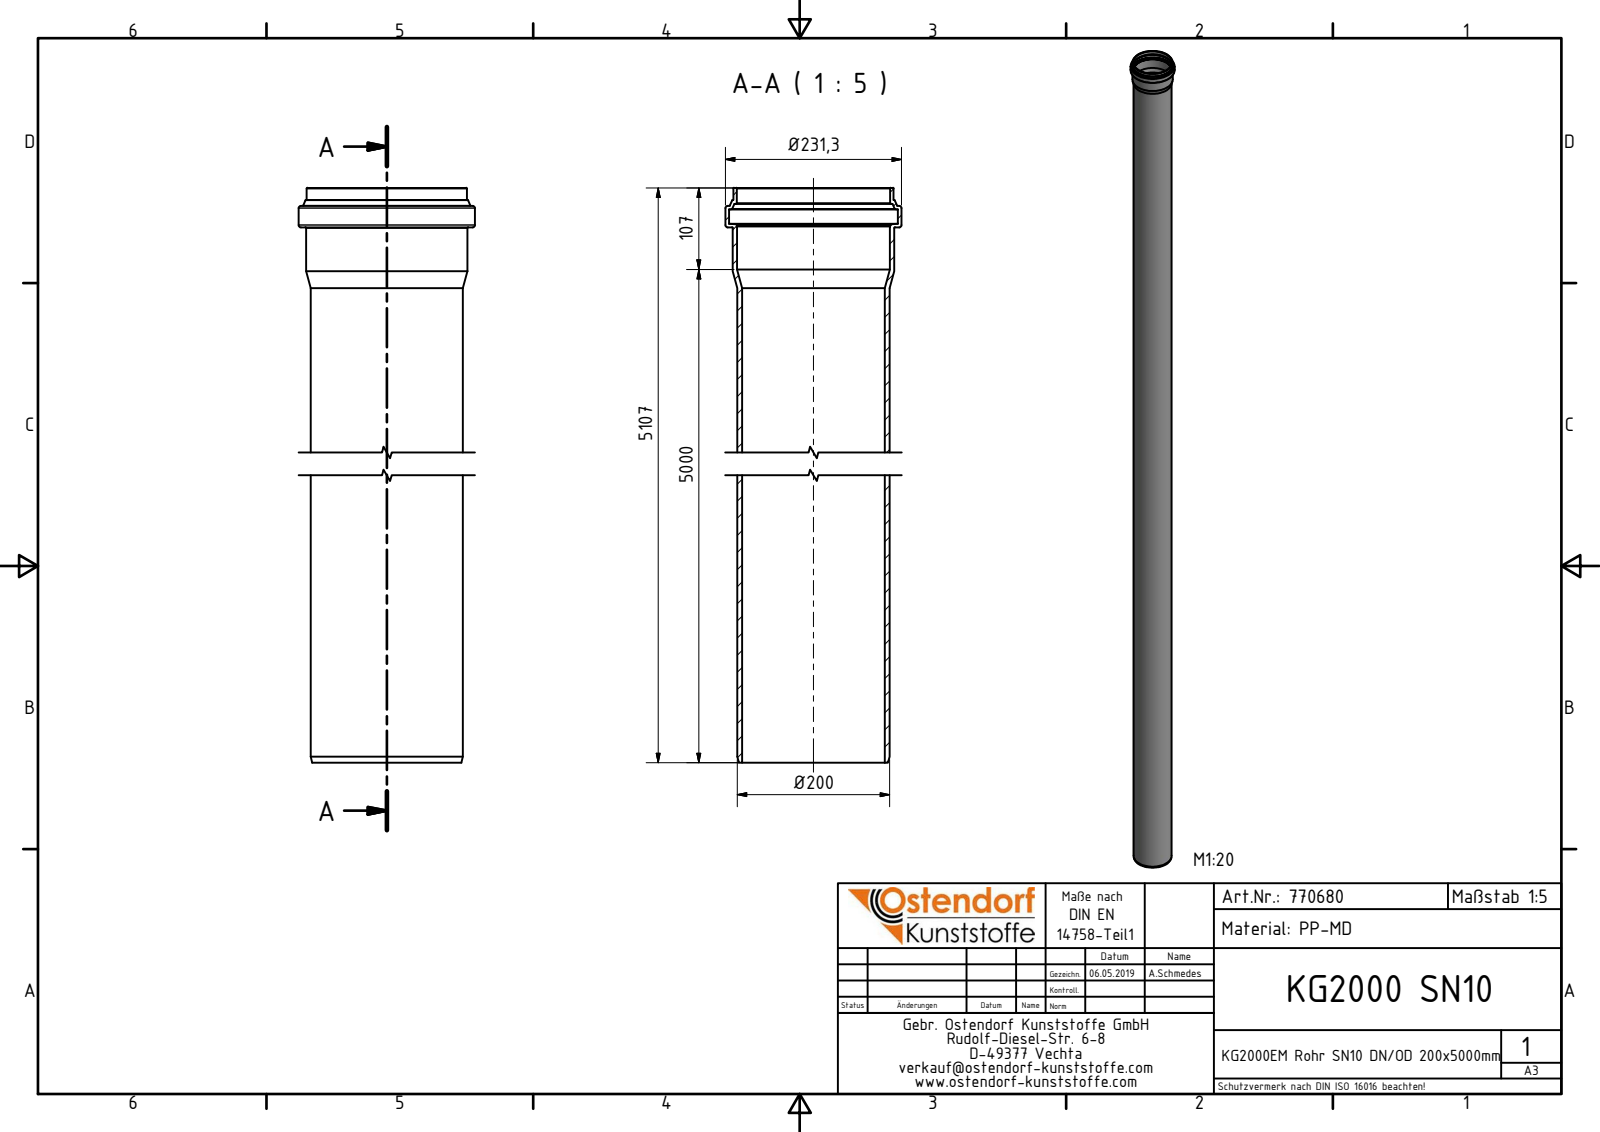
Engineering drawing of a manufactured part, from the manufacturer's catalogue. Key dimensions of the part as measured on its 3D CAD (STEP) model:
Part name (STEP PRODUCT): 770680 KG2000EM Rohr SN10 DN-OD200x5000
STEP written by: Autodesk Inventor 2016 (AUTOMOTIVE_DESIGN)
Units: millimetres
Bodies: 1 solid, 37 faces (6 planar, 9 cylindrical, 22 other)
Overall size (bounding box): 5107 × 231.3 × 231.3
Volume: 19 290 000 mm³ · Surface area: 6 258 000 mm²
Round holes (diameter × count): ⌀187.6 ×1, ⌀200.8 ×1, ⌀201 ×1, ⌀221.9 ×1
Round bosses / shafts (diameter × count): ⌀231.3 ×1, ⌀212 ×1, ⌀210.4 ×1, ⌀200 ×1
Main face-to-face distances: 5055.3, 5083.5, 28.2, 5107, 51.7, 23.5, 5090.97, 35.67, 7.47, 16.03
